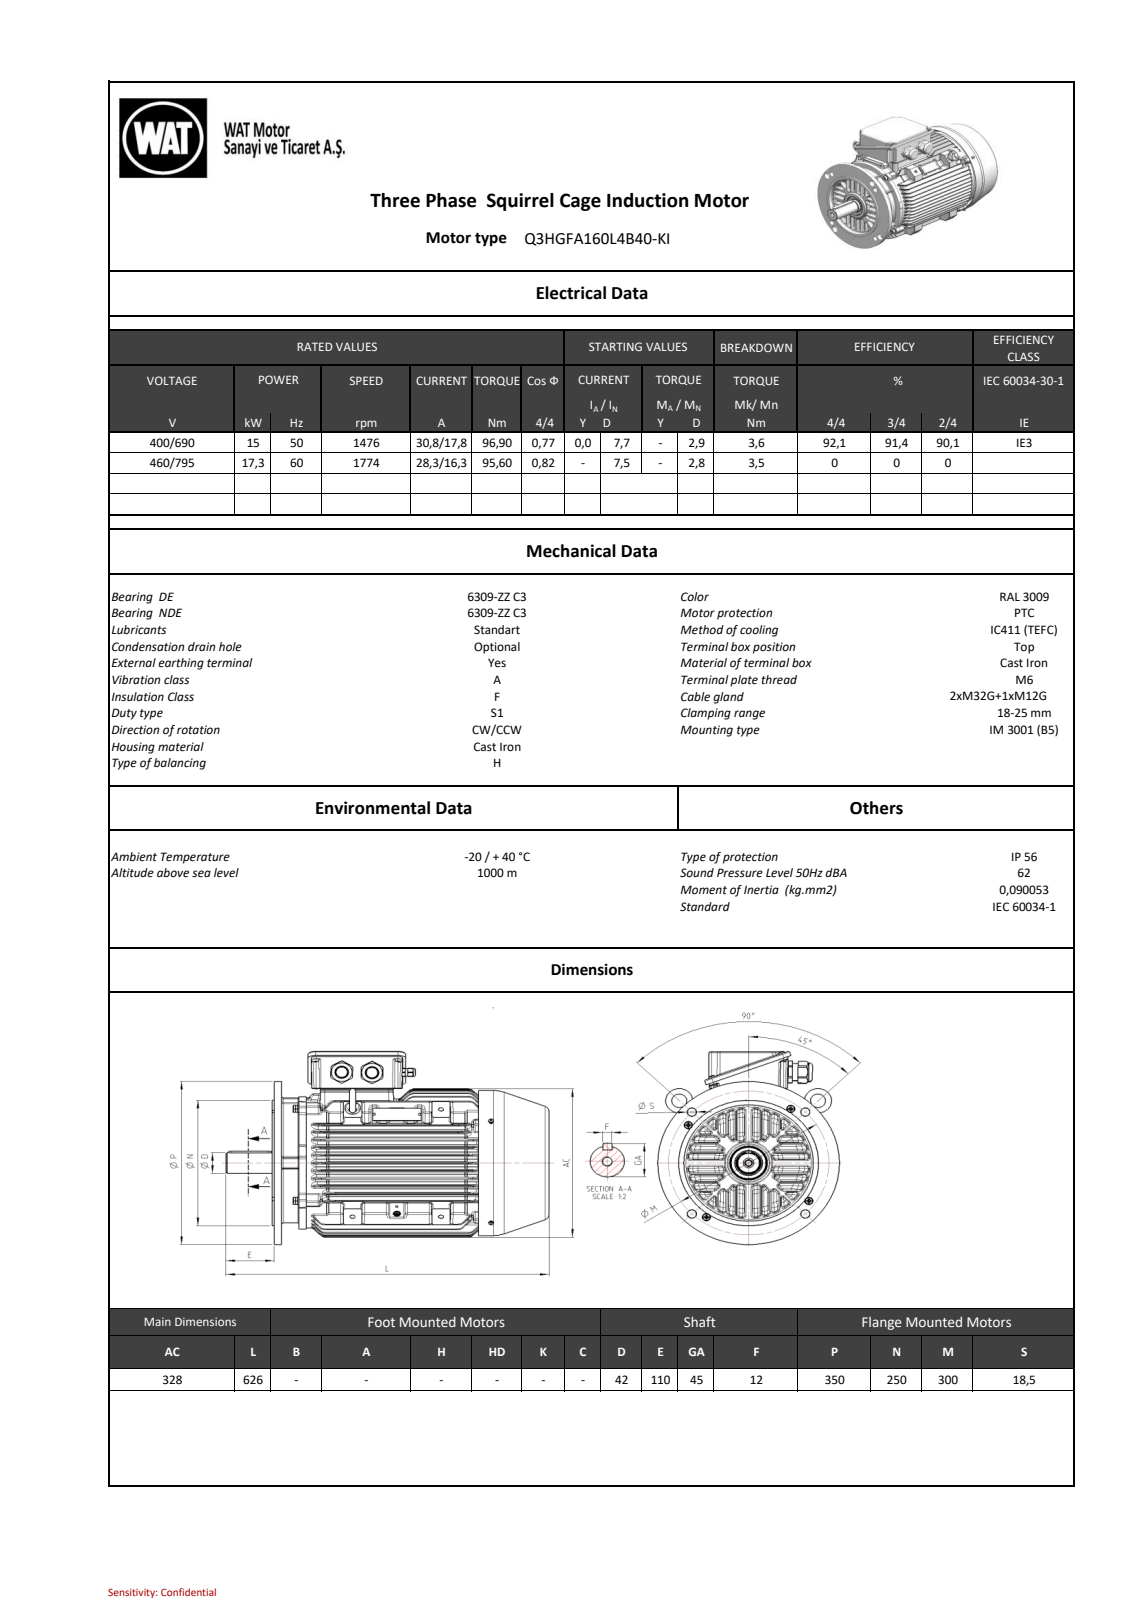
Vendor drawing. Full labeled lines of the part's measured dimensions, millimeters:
Part name (STEP PRODUCT): C9017F38B806swdk
STEP written by: SIEMENS PLM Software NX 11.0 (AUTOMOTIVE_DESIGN)
Units: millimetres
Bodies: 0 solids, 5390 faces (1026 planar, 1508 cylindrical, 2856 other)
Overall size (bounding box): 625.5 × 402.41 × 350
Round holes (diameter × count): ⌀5.5 ×8, ⌀9 ×8, ⌀4.2 ×6, ⌀10.9 ×6, ⌀5.3 ×4, ⌀18.5 ×4, ⌀23 ×4, ⌀2.5 ×2, ⌀5.2 ×2, ⌀19 ×2, ⌀21 ×2, ⌀10 ×1
Round bosses / shafts (diameter × count): ⌀16 ×8, ⌀20 ×4, ⌀34.5 ×2, ⌀31.25 ×2, ⌀30 ×2, ⌀350 ×1, ⌀317 ×1, ⌀282 ×1
Partial cylindrical surfaces — rounded edges, fillets, slot ends (radius × count): R5 ×187, R1.5 ×112, R2 ×96, R4 ×94, R3 ×79, R3.5 ×70, R1.8 ×58, R0.4 ×31
Main face-to-face distances: 15.17, 137.45, 30.42, 15.25, 122.2, 45.73, 106.89, 30.56, 15.31, 61.11
Hole centre spacings: 136, 26.31, 144, 189.04, 203.65, 225.26, 292.89, 69.72
